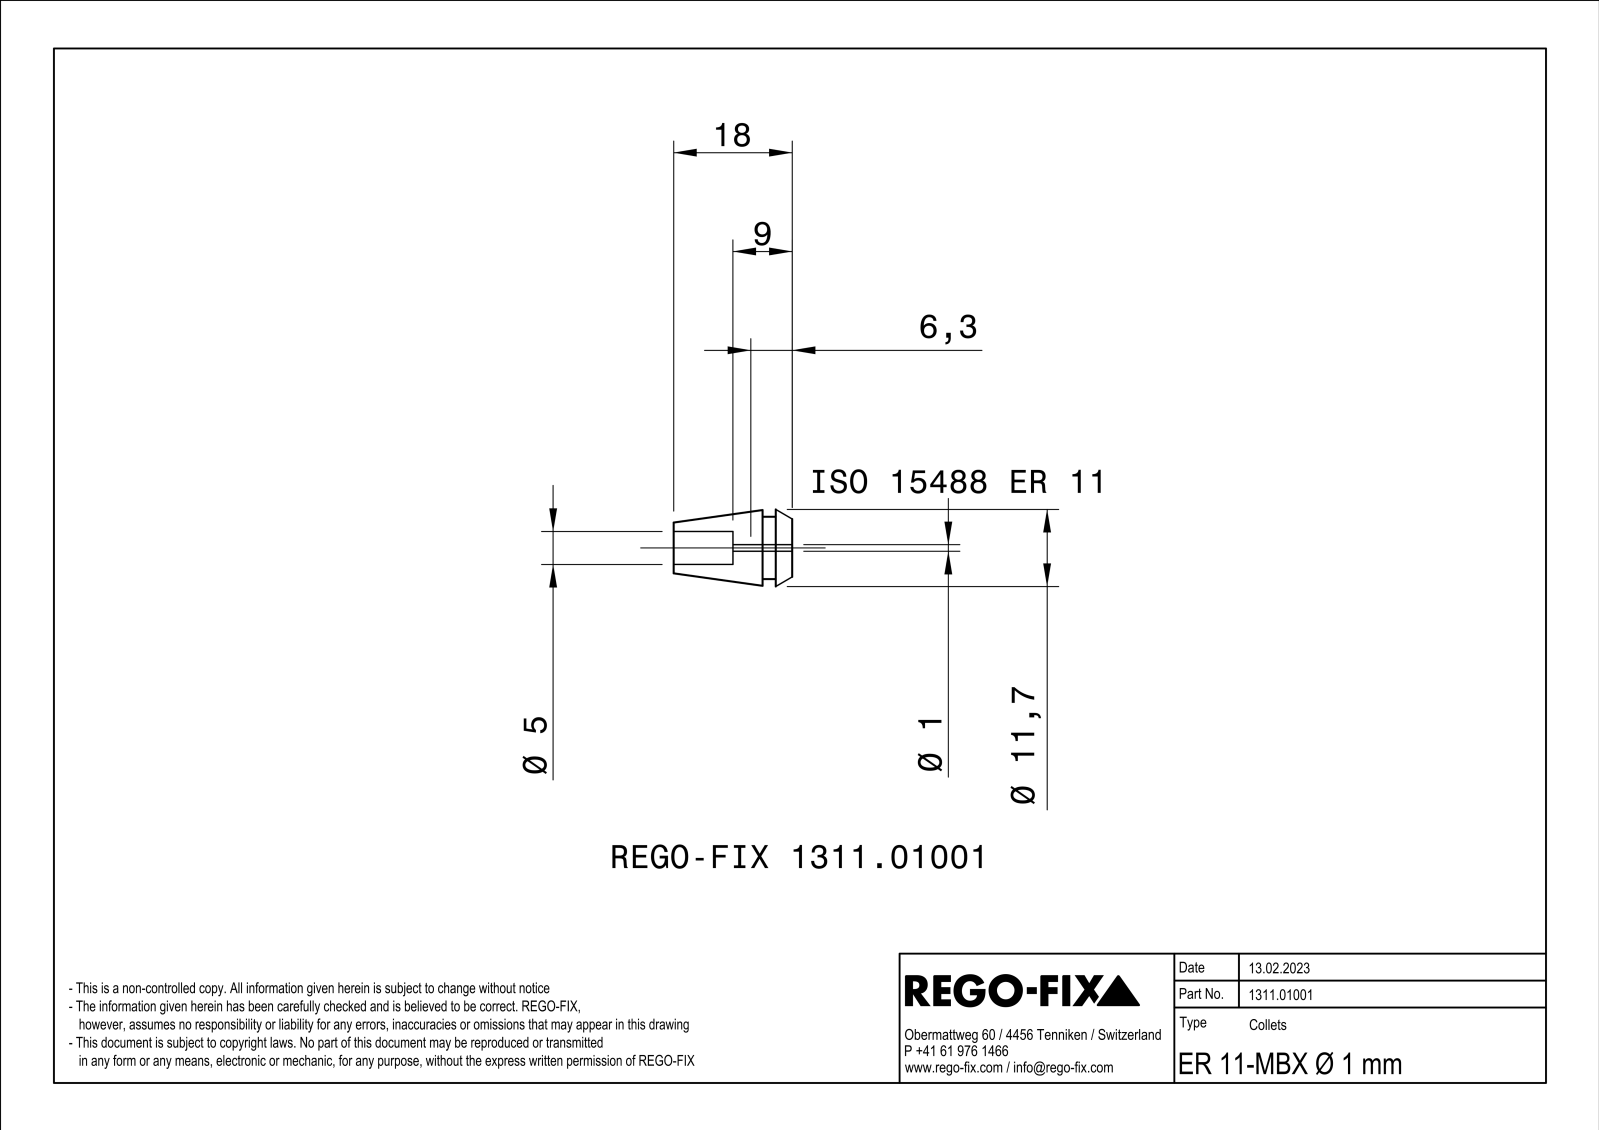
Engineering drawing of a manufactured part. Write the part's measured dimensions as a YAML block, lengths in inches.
part_name: "NOCUT"
step_written_by: "SIEMENS PLM Software Solid Edge ST10 (AUTOMOTIVE_DESIGN)"
units: inches
bodies: {solids: 1, faces: 91, planar: 26, cylindrical: 19, other: 46}
overall_size: [0.709, 0.449, 0.448]
volume: 0.06
surface_area: 1.942
round_holes:
  - {diameter: 0.059, count: 3}
  - {diameter: 0.197, count: 1}
round_bosses_or_shafts:
  - {diameter: 0.374, count: 1}
partial_cylinders:
  - {radius: 0.984, count: 3}
  - {radius: 0.02, count: 1}
face_to_face_distances: [0.031, 0.177, 0.021, 0.709, 0.531, 0.354, 0.098, 0.079, 0.61, 0.256]
hole_center_spacings: [0.067, 0.116]
